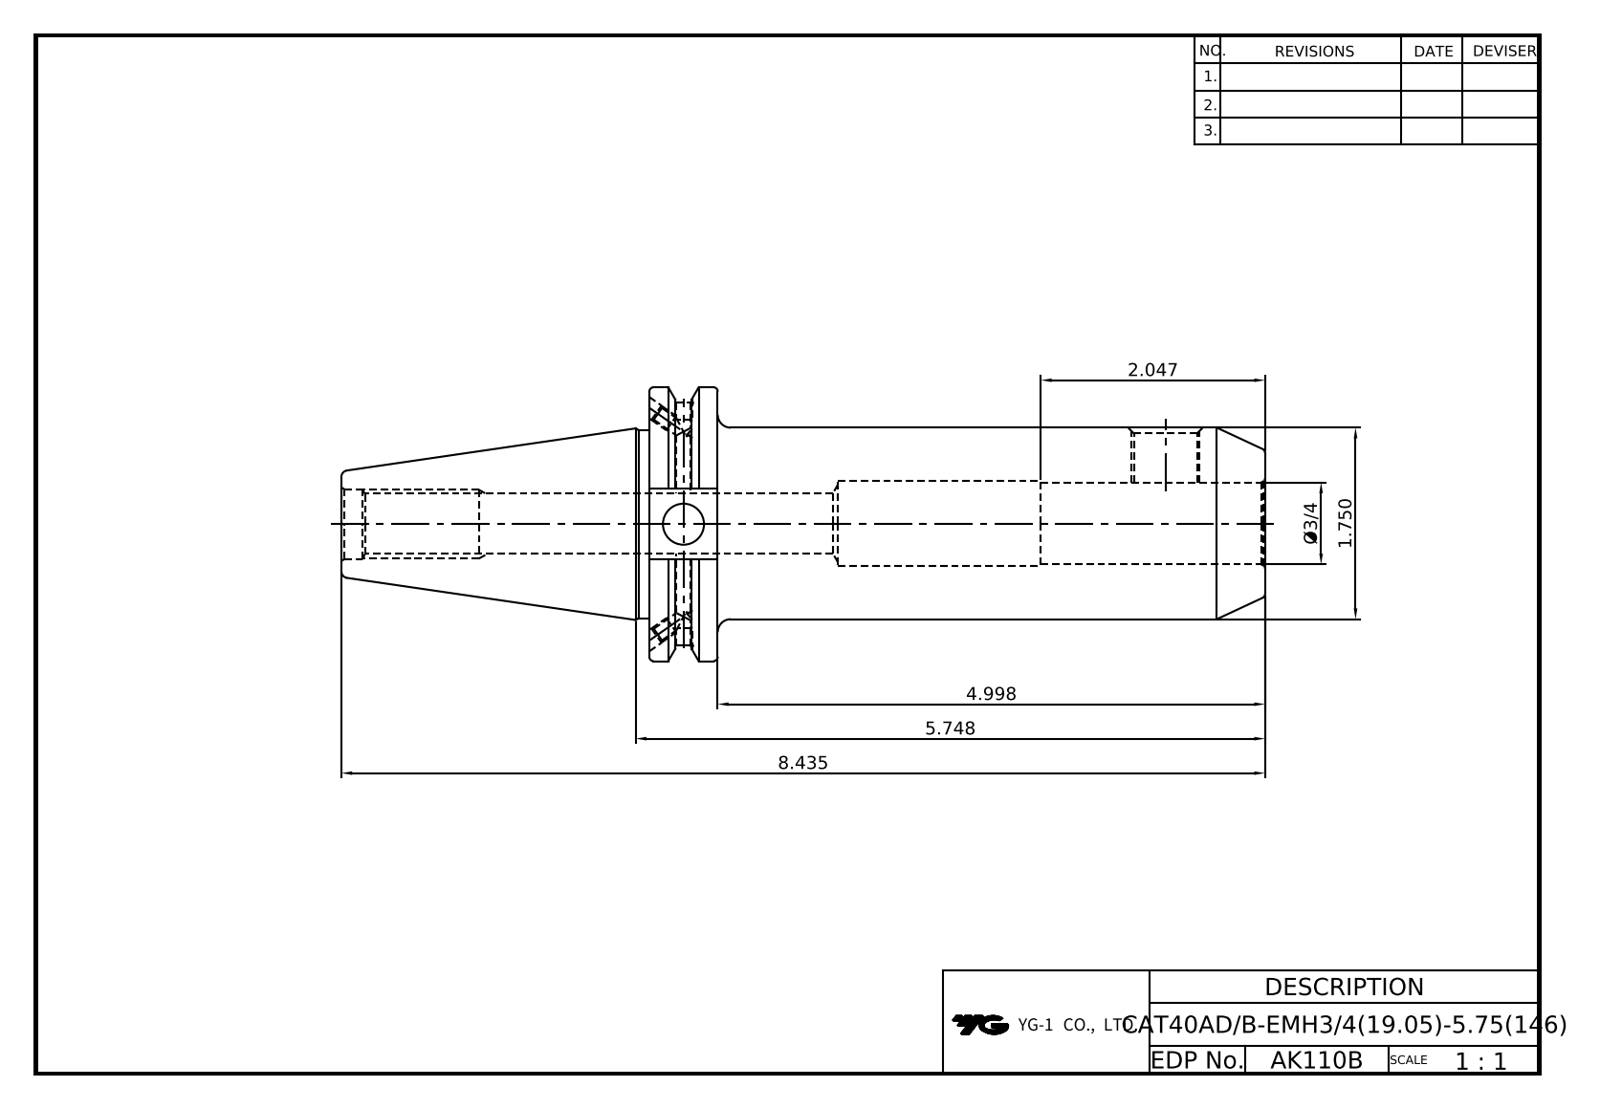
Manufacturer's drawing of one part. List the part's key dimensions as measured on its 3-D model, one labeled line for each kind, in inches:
Part name (STEP PRODUCT): LO-CAT40ADB-EMH19.05-146
STEP written by: Autodesk Inventor 2020 (AUTOMOTIVE_DESIGN)
Units: inches
Bodies: 1 solid, 91 faces (40 planar, 28 cylindrical, 23 other)
Overall size (bounding box): 8.435 × 2.5 × 2.405
Volume: 15.71 in³ · Surface area: 70.22 in²
Round holes (diameter × count): ⌀0.128 ×4, ⌀0.157 ×2, ⌀0.165 ×2, ⌀0.375 ×1, ⌀0.527 ×1, ⌀0.565 ×1, ⌀0.642 ×1, ⌀0.75 ×1, ⌀0.774 ×1
Round bosses / shafts (diameter × count): ⌀2.5 ×1, ⌀1.75 ×1, ⌀1.717 ×1
Partial cylindrical surfaces — rounded edges, fillets, slot ends (radius × count): R1.108 ×1
Main face-to-face distances: 0.625, 5.623, 4.998, 1.874, 1.723, 1.098, 3.9, 0.645, 2.812, 3.437
